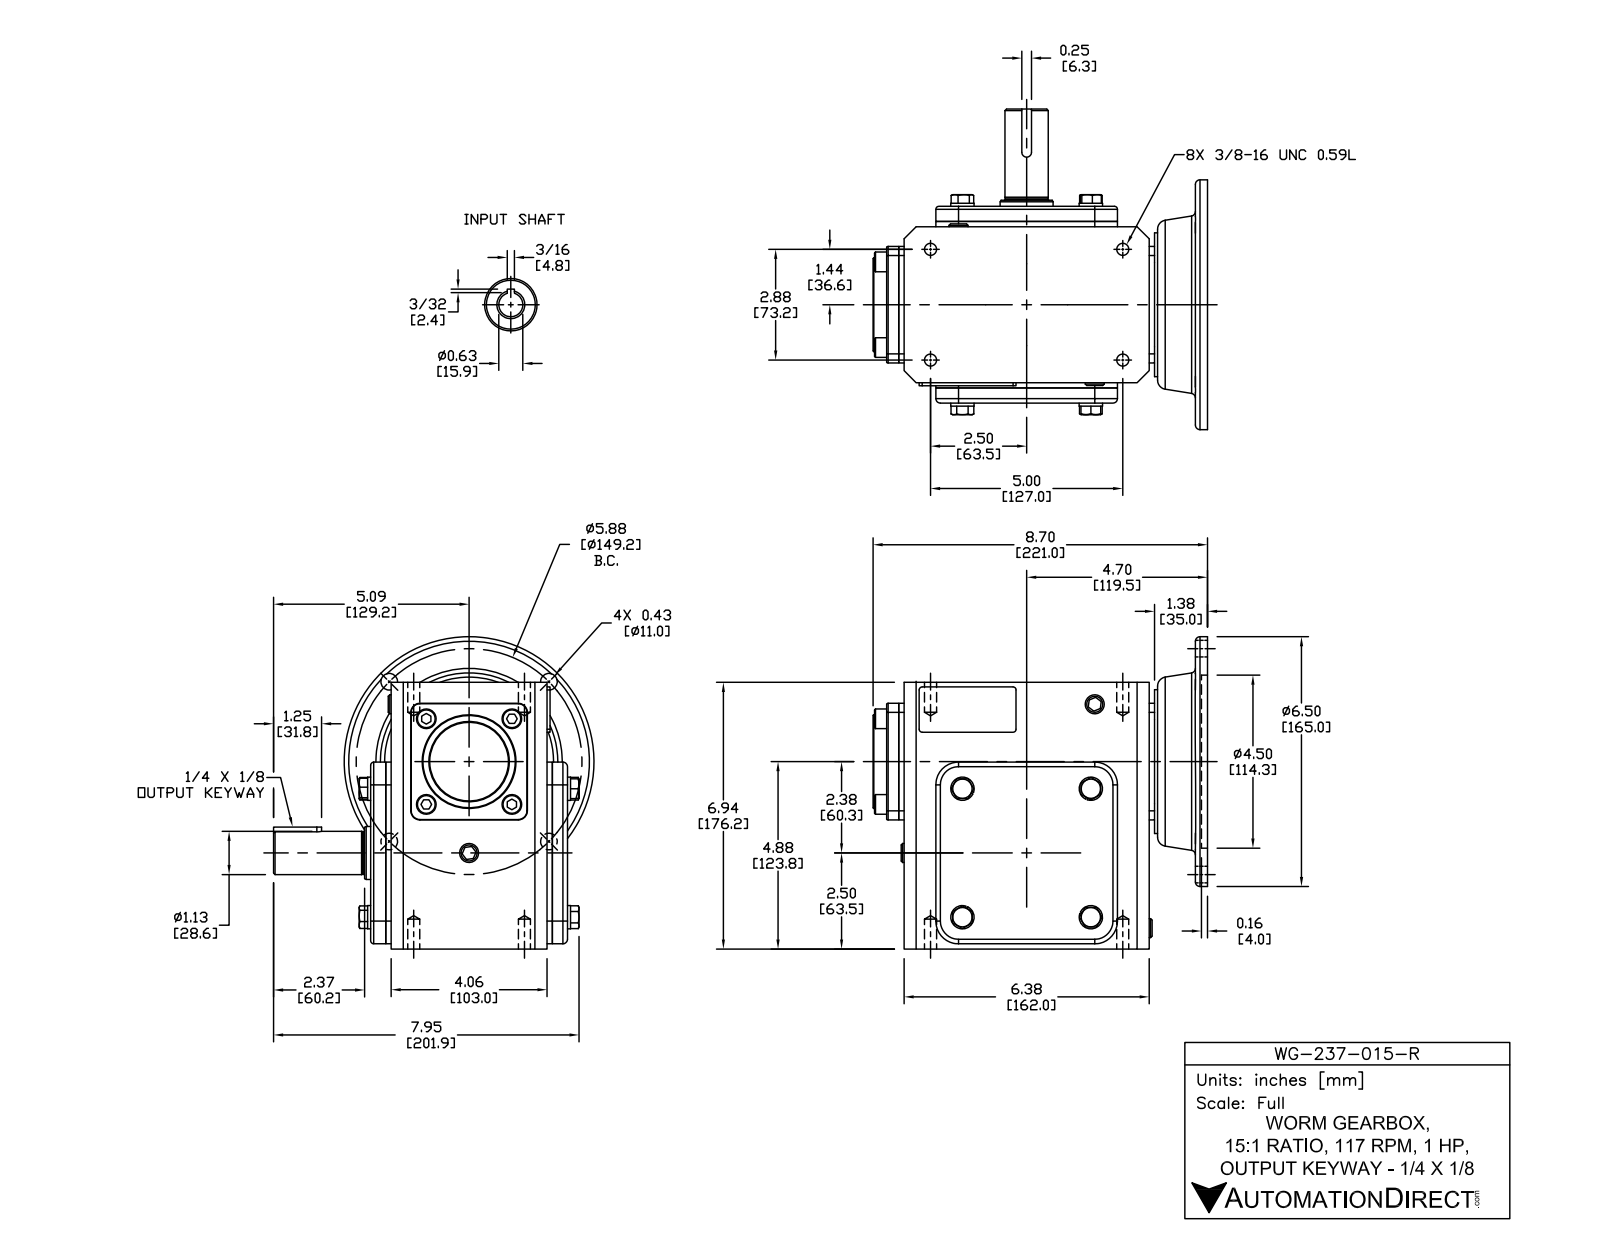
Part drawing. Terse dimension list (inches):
name: WG-237-015-R
written by: SolidWorks 2015 (CONFIG_CONTROL_DESIGN)
unit: in
bodies: 37 solids, 537 faces (294 planar, 153 cylindrical, 90 other)
size: 8.701 × 8.335 × 8.123
volume: 222.4 in³; area: 508.3 in²
holes: 4× ⌀0.313, 4× ⌀0.406, 1× ⌀0.591, 1× ⌀0.625, 1× ⌀1.378, 1× ⌀1.457, 1× ⌀1.772, 1× ⌀3.819, 1× ⌀4.5
bosses: 4× ⌀0.606, 4× ⌀0.512, 1× ⌀6.496, 1× ⌀3.74, 1× ⌀2.441, 1× ⌀2.047, 1× ⌀1.181, 1× ⌀1.142
rounds: 12× R0.079, 6× R0.236, 4× R0.118, 4× R0.591, 2× R0.02, 2× R0.039, 1× R0.125
face distances: 0.138, 4.724, 0.394, 4.331, 0.531, 4.587, 4.193, 6.516, 6.937, 0.315
hole spacings: 2.937, 2.098, 2.88, 4.154, 4.154, 4.913, 5, 5.77
